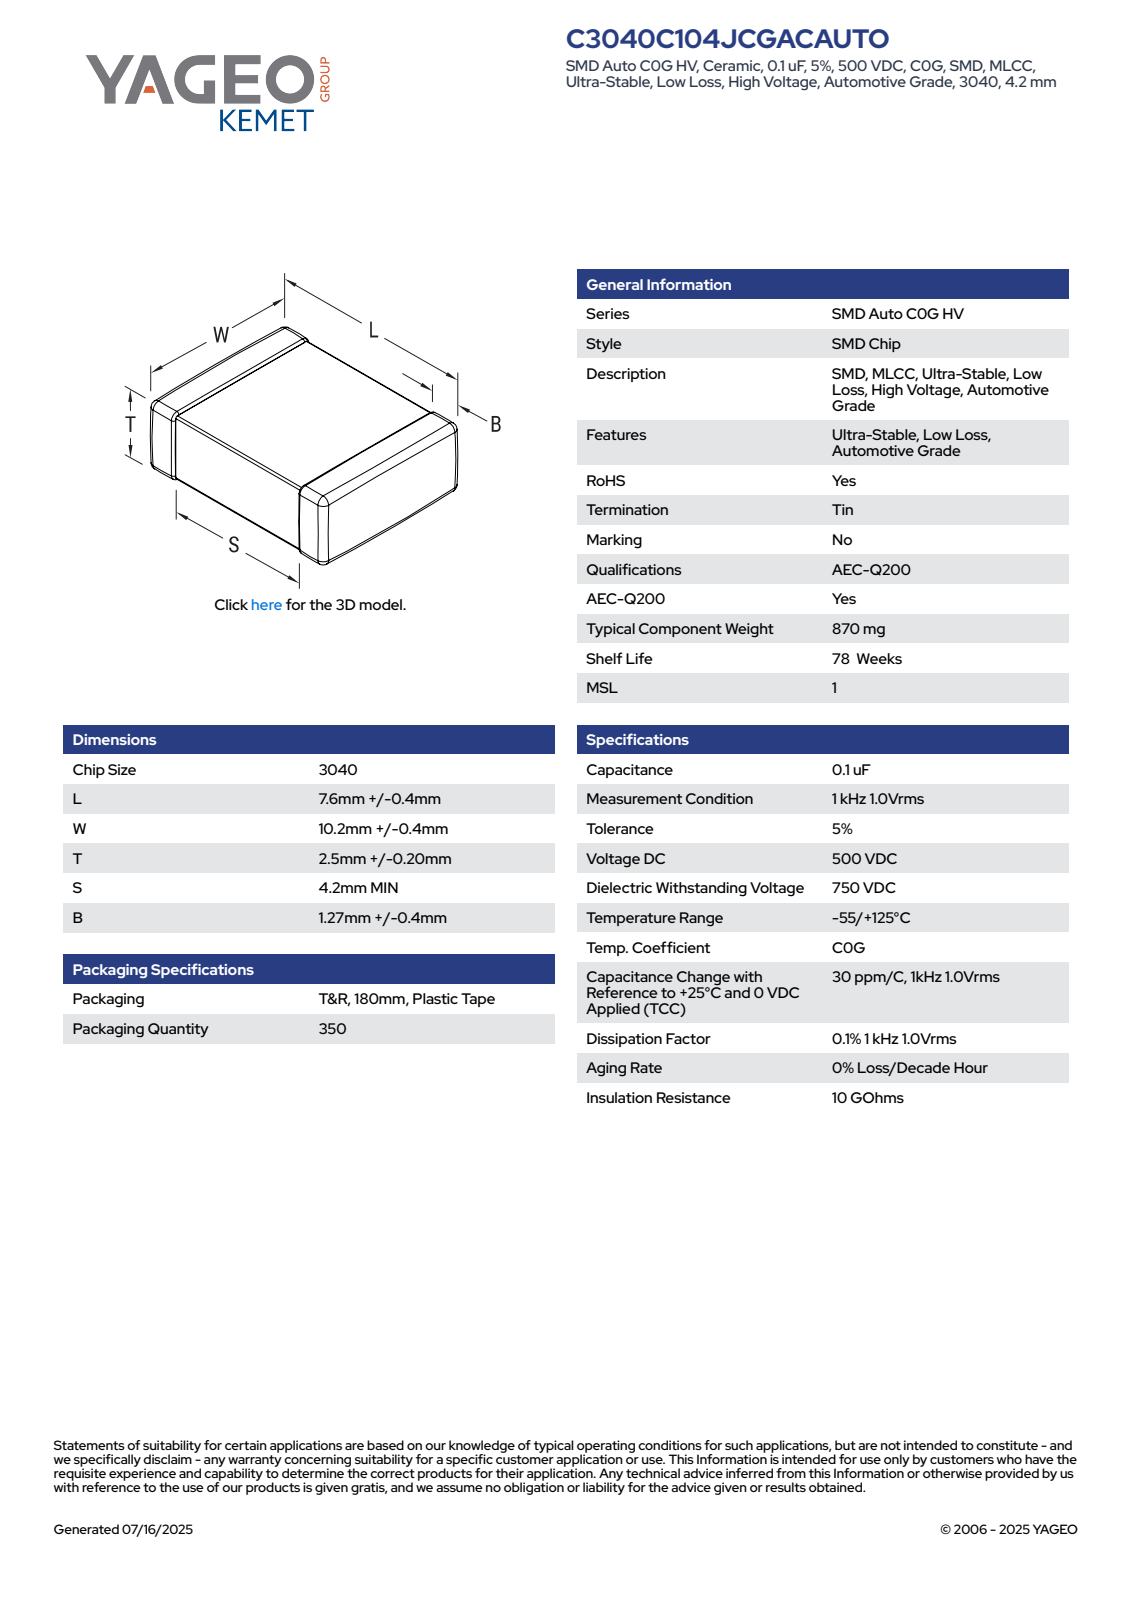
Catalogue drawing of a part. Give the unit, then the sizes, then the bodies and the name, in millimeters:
Units: millimetres
Overall size (bounding box): 10.6 × 8 × 2.7
Partial cylindrical surfaces — rounded edges, fillets, slot ends (radius × count): R0.22 ×24
Main face-to-face distances: 2.48, 2.26, 2.7, 8, 10.38, 10.16, 10.6, 5.51, 5.29, 4.87
Volume: 201 mm³ · Surface area: 262 mm²
Bodies: 4 solids, 121 faces (71 planar, 34 cylindrical, 16 other)
Part name (STEP PRODUCT): CCS_CCSTDNOS_3040_L8W10.6T2.7B1.67
STEP written by: SolidWorks 2014 (AUTOMOTIVE_DESIGN)
